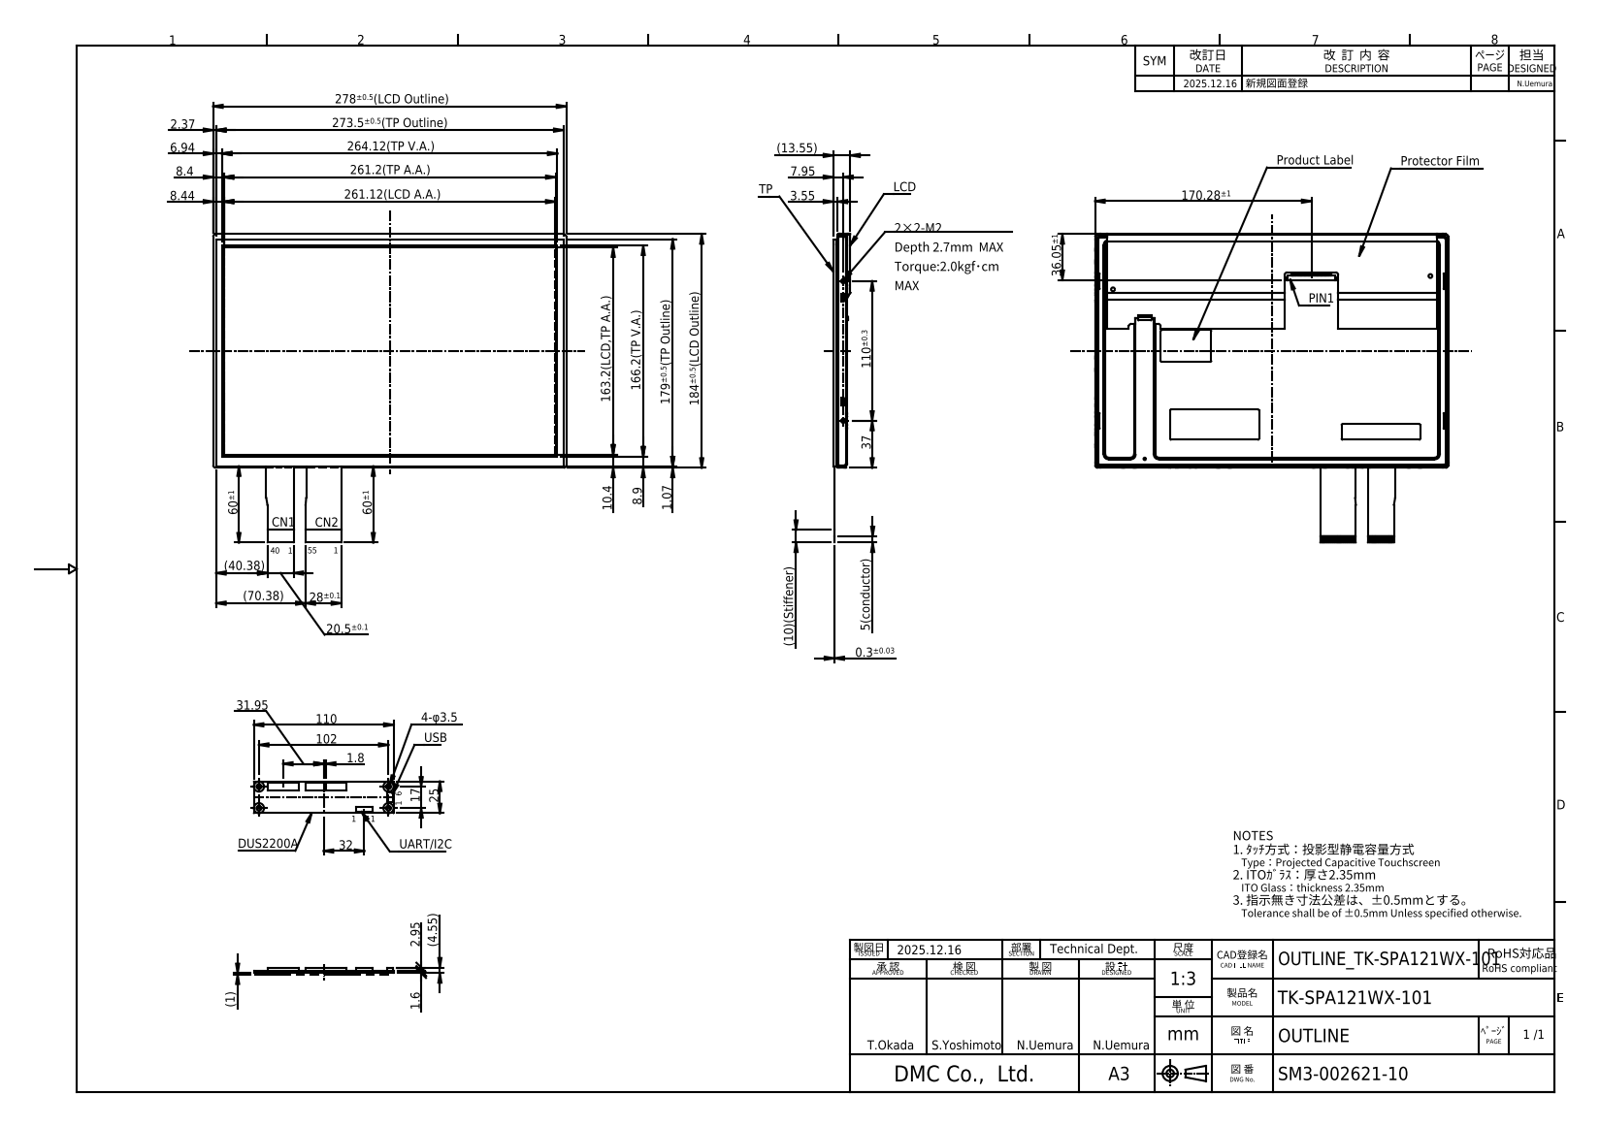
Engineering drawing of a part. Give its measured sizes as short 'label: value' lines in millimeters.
name: TK-SPA121WX-101
written by: Autodesk Inventor 2024 (AUTOMOTIVE_DESIGN)
unit: mm
bodies: 1 solid, 4754 faces (3343 planar, 1088 cylindrical, 323 other)
size: 278 × 242.98 × 13.54
volume: 271 767 mm³; area: 310 037 mm²
holes: 4× ⌀1, 4× ⌀2, 3× ⌀1.8, 2× ⌀3, 2× ⌀3.2, 2× ⌀5.03
bosses: 4× ⌀4, 2× ⌀3, 1× ⌀2.1
rounds: 191× R0.5, 154× R1, 147× R0.2, 129× R0.3, 95× R0.1, 39× R0.4, 36× R0.9, 33× R0.8
face distances: 0.8, 4.28, 4.88, 9.16, 5.68, 9.96, 3.43, 0.9, 9.11, 4.23
hole spacings: 180.1, 274.1, 327.97, 4, 10.95, 11.45, 12.13, 23.39
